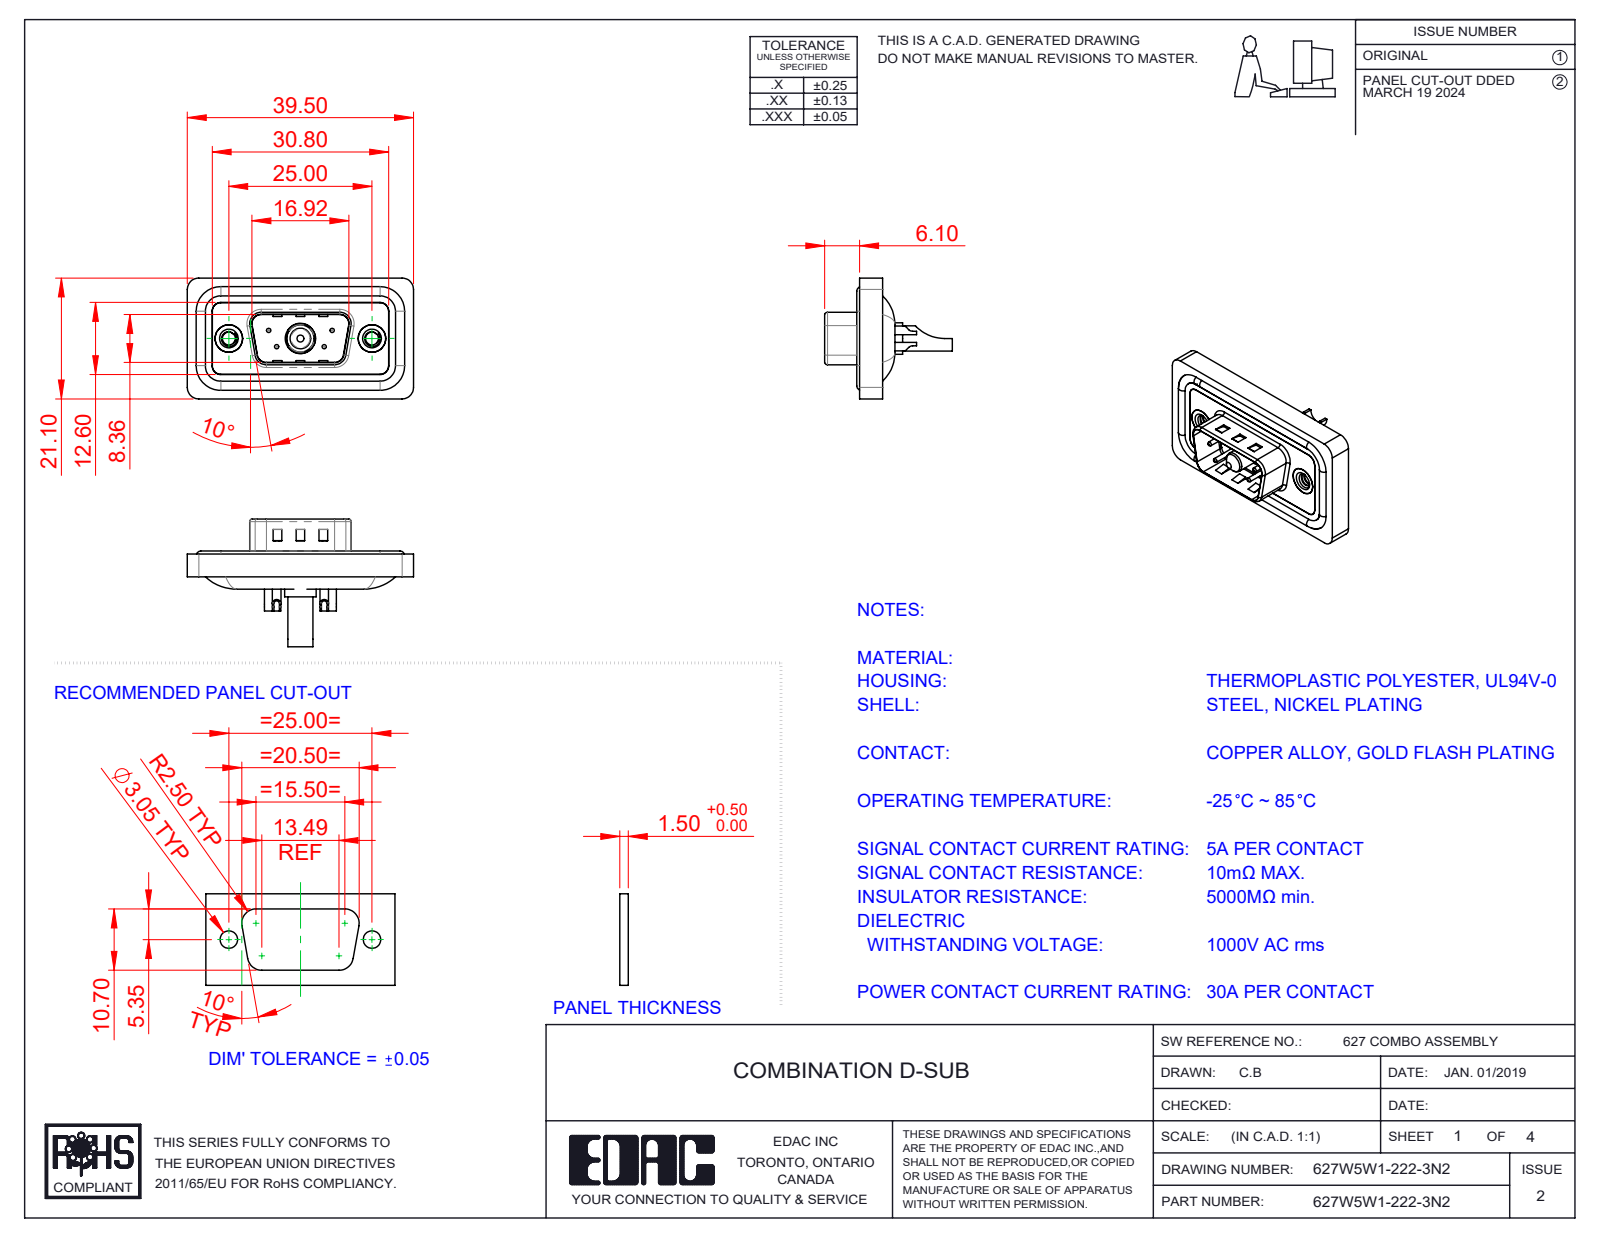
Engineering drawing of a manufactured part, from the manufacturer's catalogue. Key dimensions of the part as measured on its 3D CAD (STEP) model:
Part name (STEP PRODUCT): 627Combo Threaded Rivet_2; 627Combo Waterproof Housing_09 Contacts; Power Pin_30A SC; 627Combo Shell Rear_09 Contacts (+5 more)
STEP written by: SolidWorks 2023 (CONFIG_CONTROL_DESIGN)
Units: millimetres
Bodies: 13 solids, 604 faces (194 planar, 266 cylindrical, 144 other)
Overall size (bounding box): 39.5 × 22.3 × 21.1
Volume: 4 418 mm³ · Surface area: 7 081 mm²
Round holes (diameter × count): ⌀0.75 ×4, ⌀1 ×4, ⌀1.6 ×4, ⌀2 ×4, ⌀2.26 ×2, ⌀4 ×2, ⌀4.8 ×2, ⌀5 ×2, ⌀3.5 ×1, ⌀4.85 ×1, ⌀5.3 ×1
Round bosses / shafts (diameter × count): ⌀1.6 ×4, ⌀1.5 ×4, ⌀4.9 ×2, ⌀5.5 ×1, ⌀5.2 ×1, ⌀4.75 ×1, ⌀4.4 ×1, ⌀3.75 ×1
Partial cylindrical surfaces — rounded edges, fillets, slot ends (radius × count): R1.5 ×22, R2 ×18, R0.5 ×8, R1.6 ×8, R1 ×6, R0.25 ×4, R0.6 ×4, R0.65 ×4
Main face-to-face distances: 0.4, 1.1, 2.9, 1.6, 3.1, 0.5, 1.5, 2.5, 4, 0.8
Hole centre spacings: 3.16, 5.72, 7.1, 12.5, 18.1, 4.39, 4.4, 8.31
